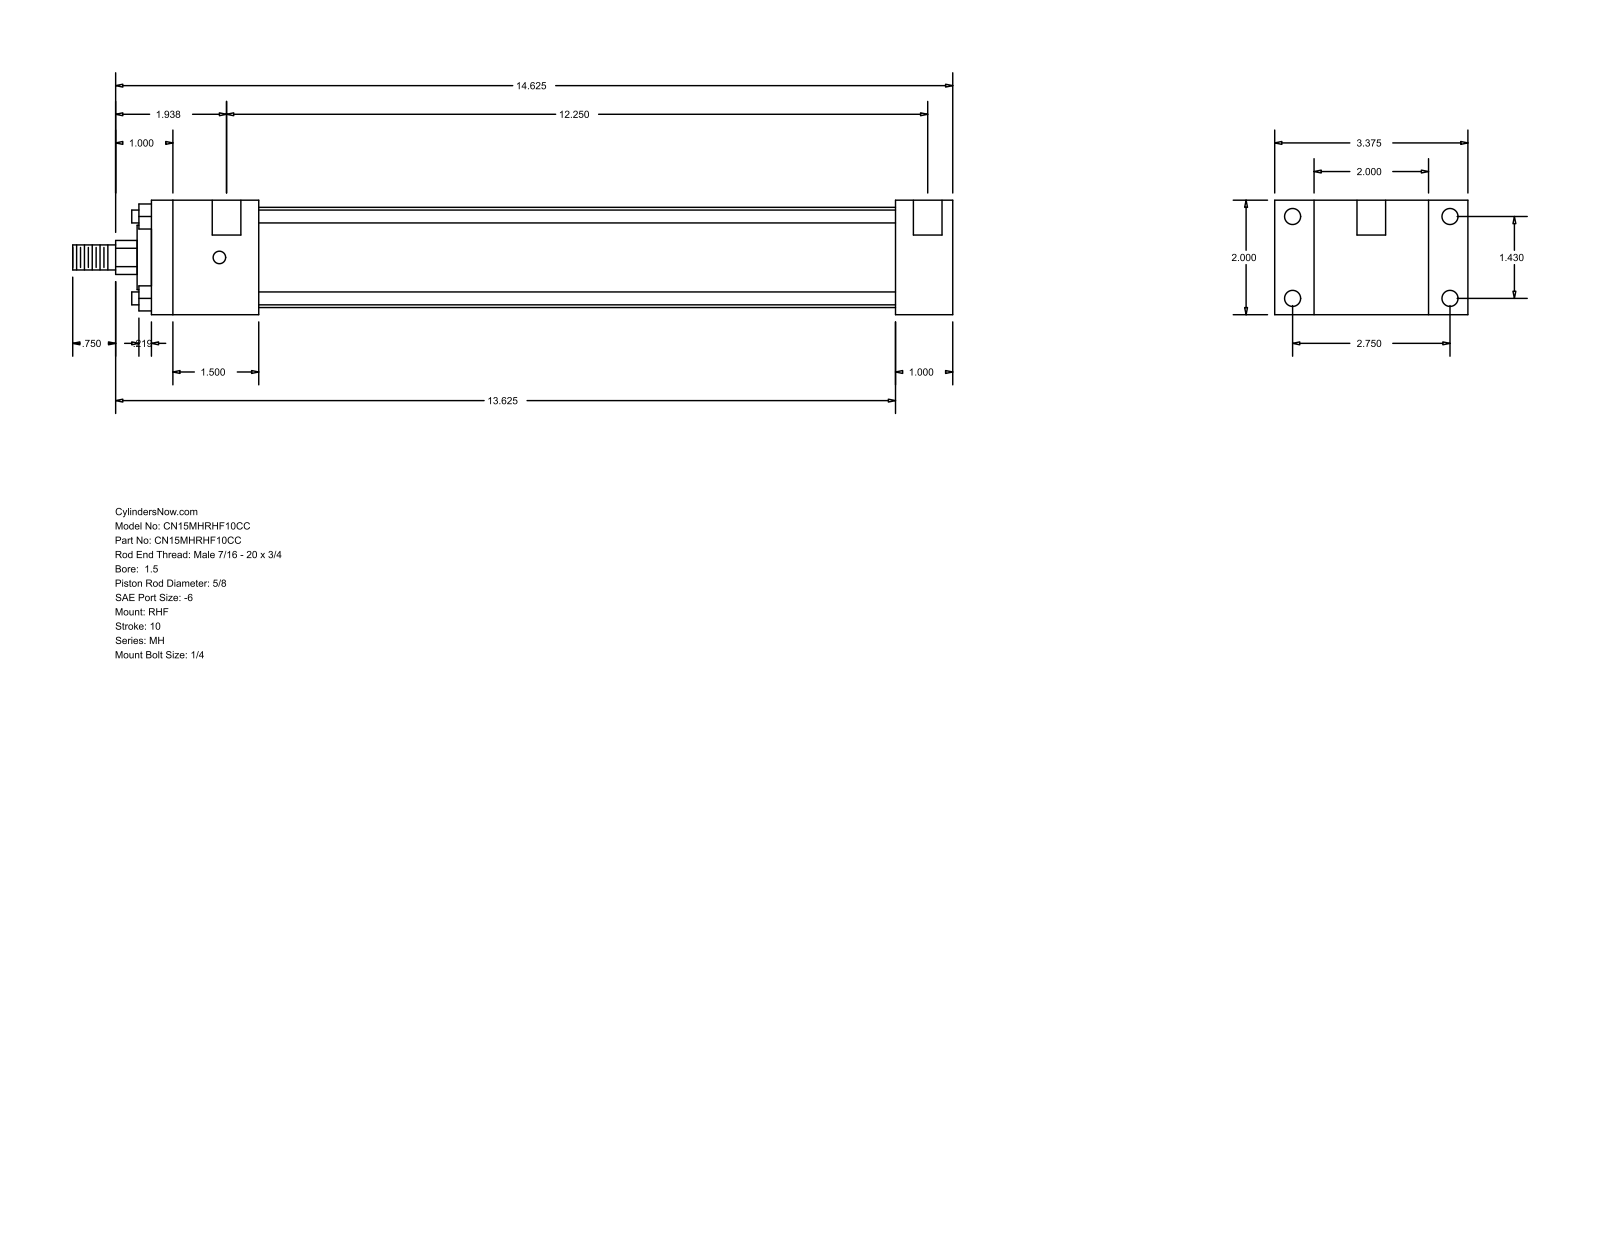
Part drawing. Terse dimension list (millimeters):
name: MH_RHF__0150_0.625
written by: GSSL Pune (CONFIG_CONTROL_DESIGN)
unit: mm
bodies: 0 solids, 88 faces (60 planar, 28 cylindrical, 0 other)
size: 390.52 × 85.72 × 50.8
holes: 4× ⌀5.56, 4× ⌀7.14, 2× ⌀12.7
bosses: 4× ⌀5.71, 1× ⌀44.45, 1× ⌀28.57, 1× ⌀15.88, 1× ⌀11.11
rounds: 1× R7.54
face distances: 50.8, 17.46, 68.26, 25.41, 330.19, 355.6, 85.72, 47.62, 282.57, 307.98
hole spacings: 36.32, 69.84, 78.72, 314.32, 3.17, 311.15
